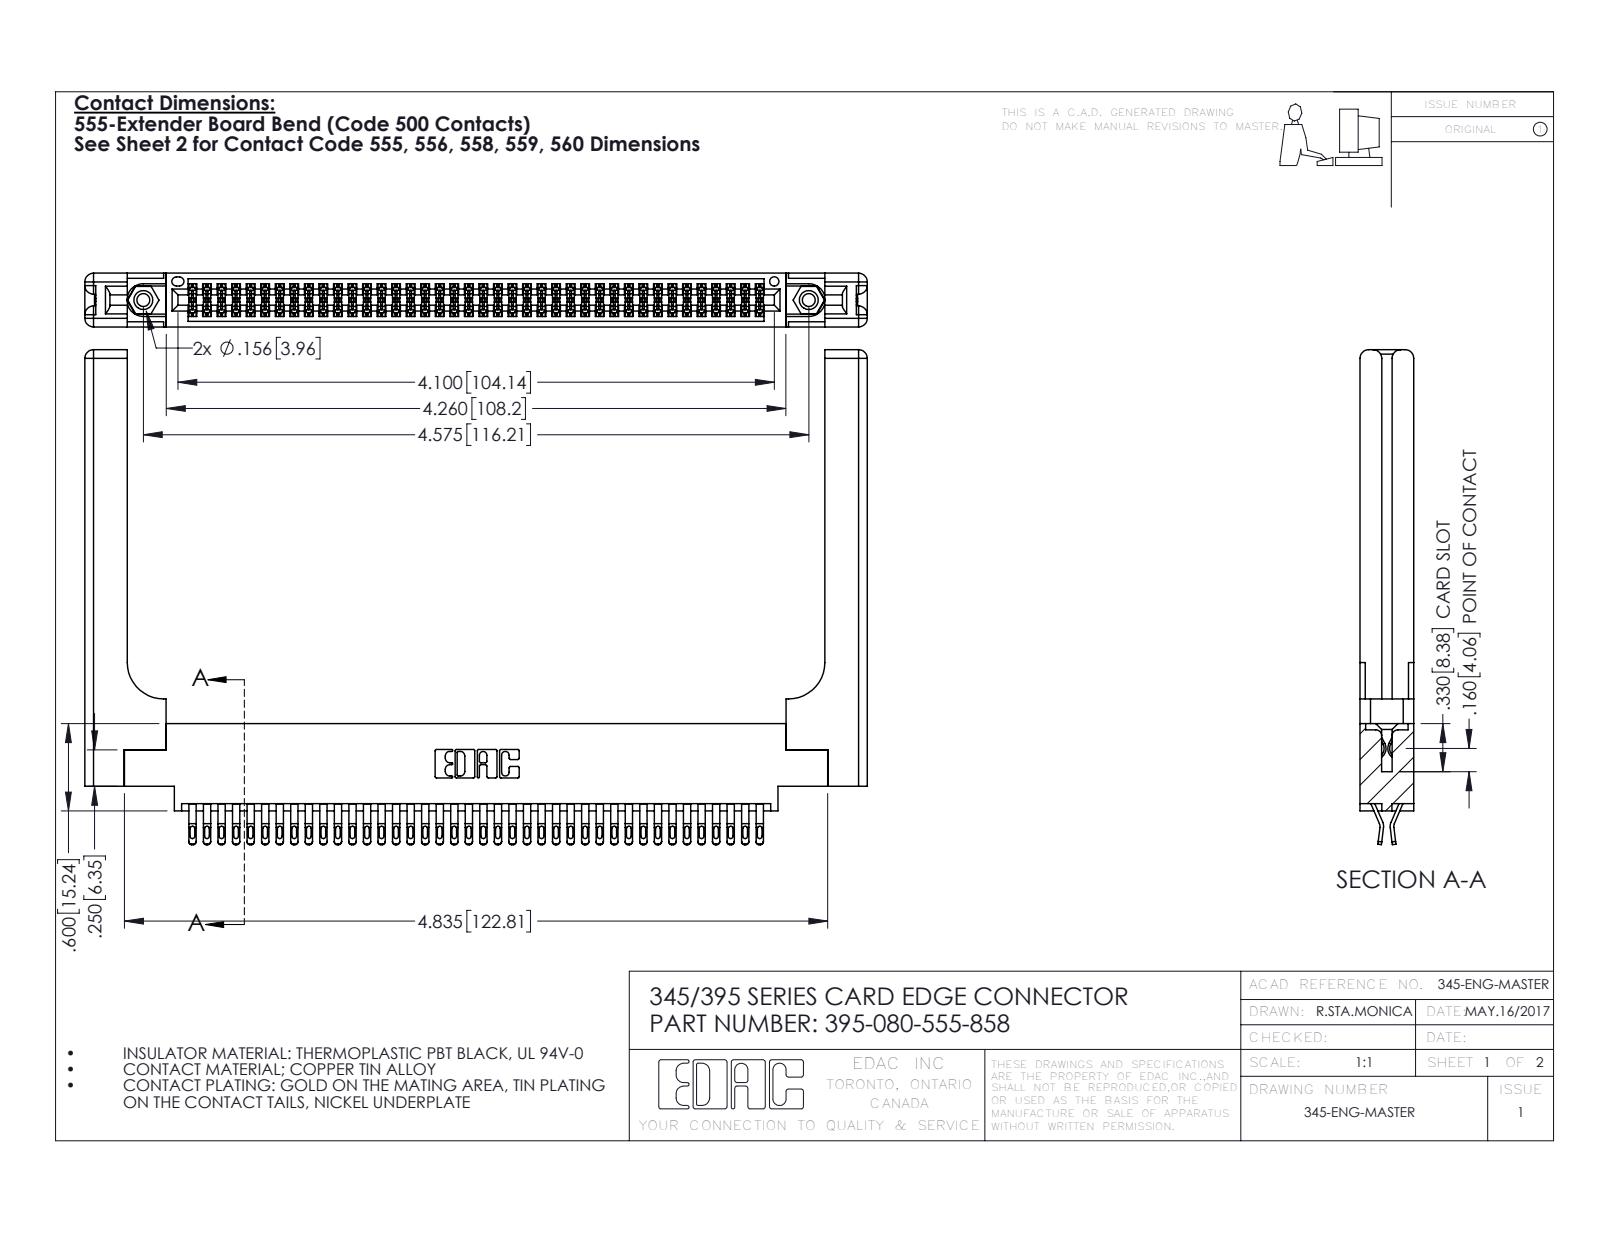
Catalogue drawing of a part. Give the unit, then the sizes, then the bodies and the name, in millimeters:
Units: millimetres
Overall size (bounding box): 136.6 × 86.4 × 9.4
Round holes (diameter × count): ⌀2.3 ×2, ⌀3.2 ×2, ⌀4 ×2, ⌀1.6 ×1
Round bosses / shafts (diameter × count): ⌀3.9 ×2
Partial cylindrical surfaces — rounded edges, fillets, slot ends (radius × count): R0.4 ×200, R0.5 ×160, R0.2 ×120, R0.3 ×22, R1.5 ×16, R0.2 ×6, R0.8 ×6, R0.7 ×3
Main face-to-face distances: 9.4, 1.8, 7.6, 0.6, 2.5, 6.9, 5.1, 5.7, 3.8, 3.8
Hole centre spacings: 6.9, 110.2, 116.2
Volume: 21 840 mm³ · Surface area: 25 740 mm²
Bodies: 85 solids, 4866 faces (2712 planar, 2094 cylindrical, 60 other)
Part name (STEP PRODUCT): 345-250-001_345-250-001-102; 345-220-058_345-220-058; 345 Part_0.170 Offset - 0.156 Dia-TH; 395-080-555-858 (+1 more)
STEP written by: SolidWorks 2016 (CONFIG_CONTROL_DESIGN)
